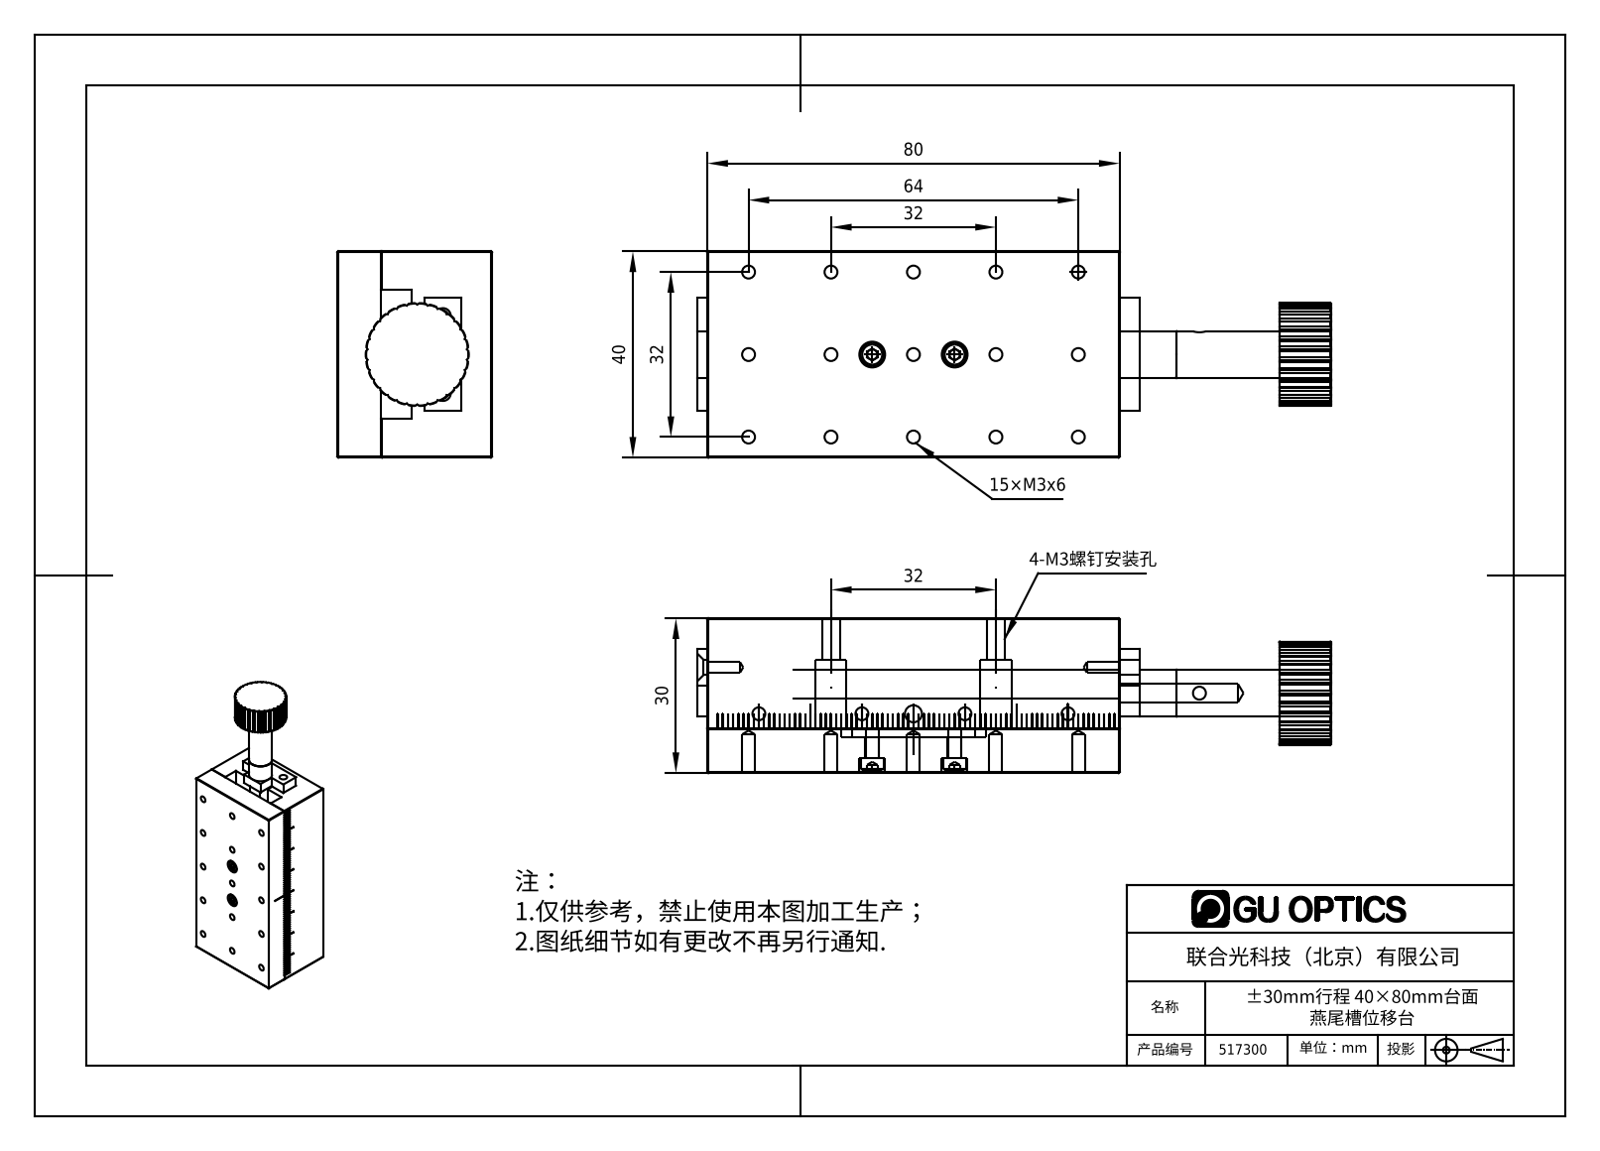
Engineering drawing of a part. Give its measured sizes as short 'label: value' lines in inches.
name: 517300
written by: SolidWorks 2016 (AUTOMOTIVE_DESIGN)
unit: in
bodies: 8 solids, 747 faces (496 planar, 135 cylindrical, 116 other)
size: 4.843 × 1.575 × 1.181
volume: 5.014 in³; area: 43.65 in²
holes: 20× ⌀0.098, 4× ⌀0.134, 4× ⌀0.236, 2× ⌀0.081, 2× ⌀0.106, 2× ⌀0.114, 2× ⌀0.118, 2× ⌀0.197, 1× ⌀0.13, 1× ⌀0.138
bosses: 2× ⌀0.177, 2× ⌀0.098, 1× ⌀0.354
rounds: 4× R0.079, 1× R0.394
face distances: 1.181, 0.846, 0.335, 1.575, 0.295, 0.394, 0.61, 0.236, 0.984, 0.571
hole spacings: 0.63, 1.409, 0.891, 1.26, 0.704, 1.135, 1.992, 1.781
